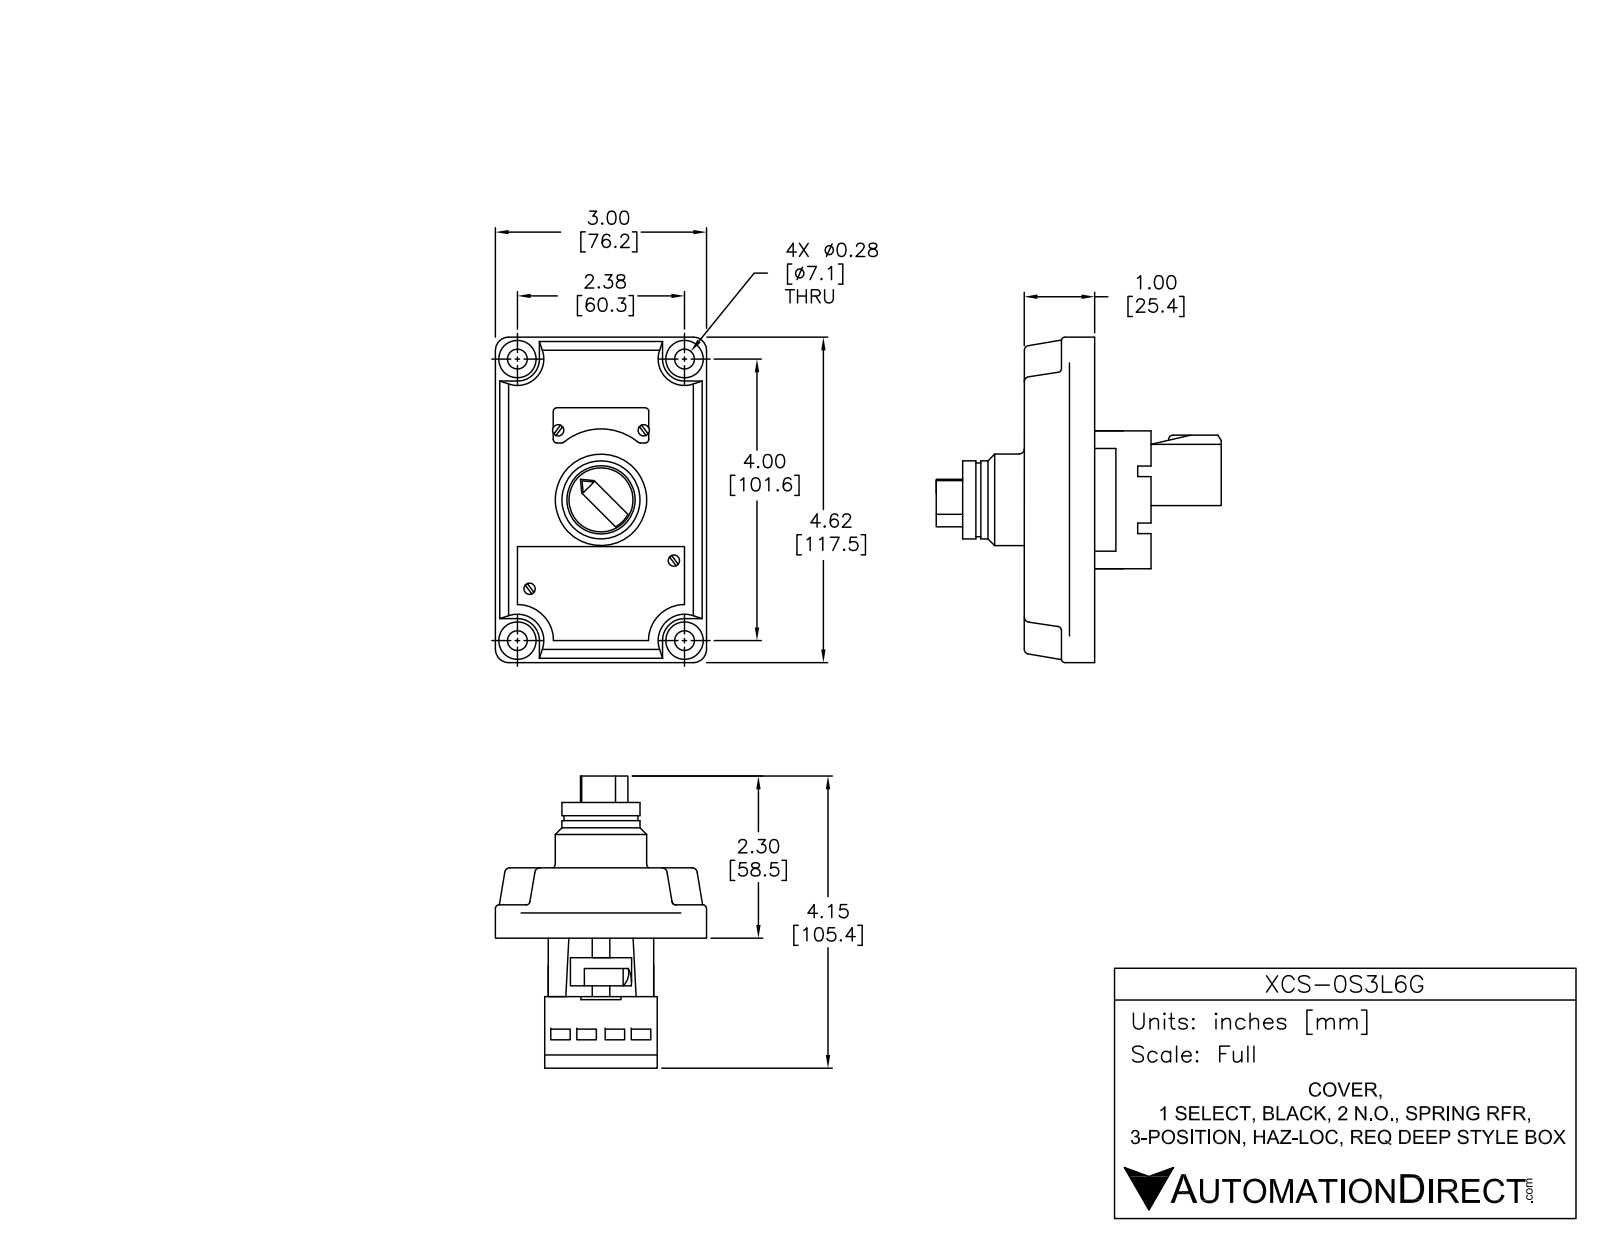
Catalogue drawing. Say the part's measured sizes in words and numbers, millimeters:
The part is named "XCS-0S3L6G". Its 3-D file was written by "SolidWorks 2015 (AUTOMOTIVE_DESIGN)". It is 11 solids with 490 faces: 181 planar, 179 cylindrical and 130 other. Overall it measures 117.6 by 94.14 by 78.74 millimeters. Its volume is 210 810 cubic millimeters and its surface area 59 522 square millimeters. Round holes: 4 of diameter 6.65, 4 of diameter 6.86, 1 of diameter 24.64. Round bosses or shafts: 6 of diameter 3.3, 4 of diameter 11.6, 4 of diameter 6.35, 1 of diameter 33.02, 1 of diameter 28.19, 1 of diameter 26.67, 1 of diameter 23.11. Partial cylindrical surfaces (rounded edges, fillets, slot ends): 28 of radius 0.25, 10 of radius 1.27, 8 of radius 0.51, 8 of radius 1.4, 8 of radius 3, 4 of radius 2.38, 4 of radius 2.54, 4 of radius 9.65. The main face-to-face distances are 13.34, 12.7, 26.04, 11.3, 24, 37.34, 17.5, 6.5, 4.8, 30.84. The hole center spacings are 59.11, 10.2, 20.4, 60.46, 101.6, 118.23, 10.13, 10.18.
